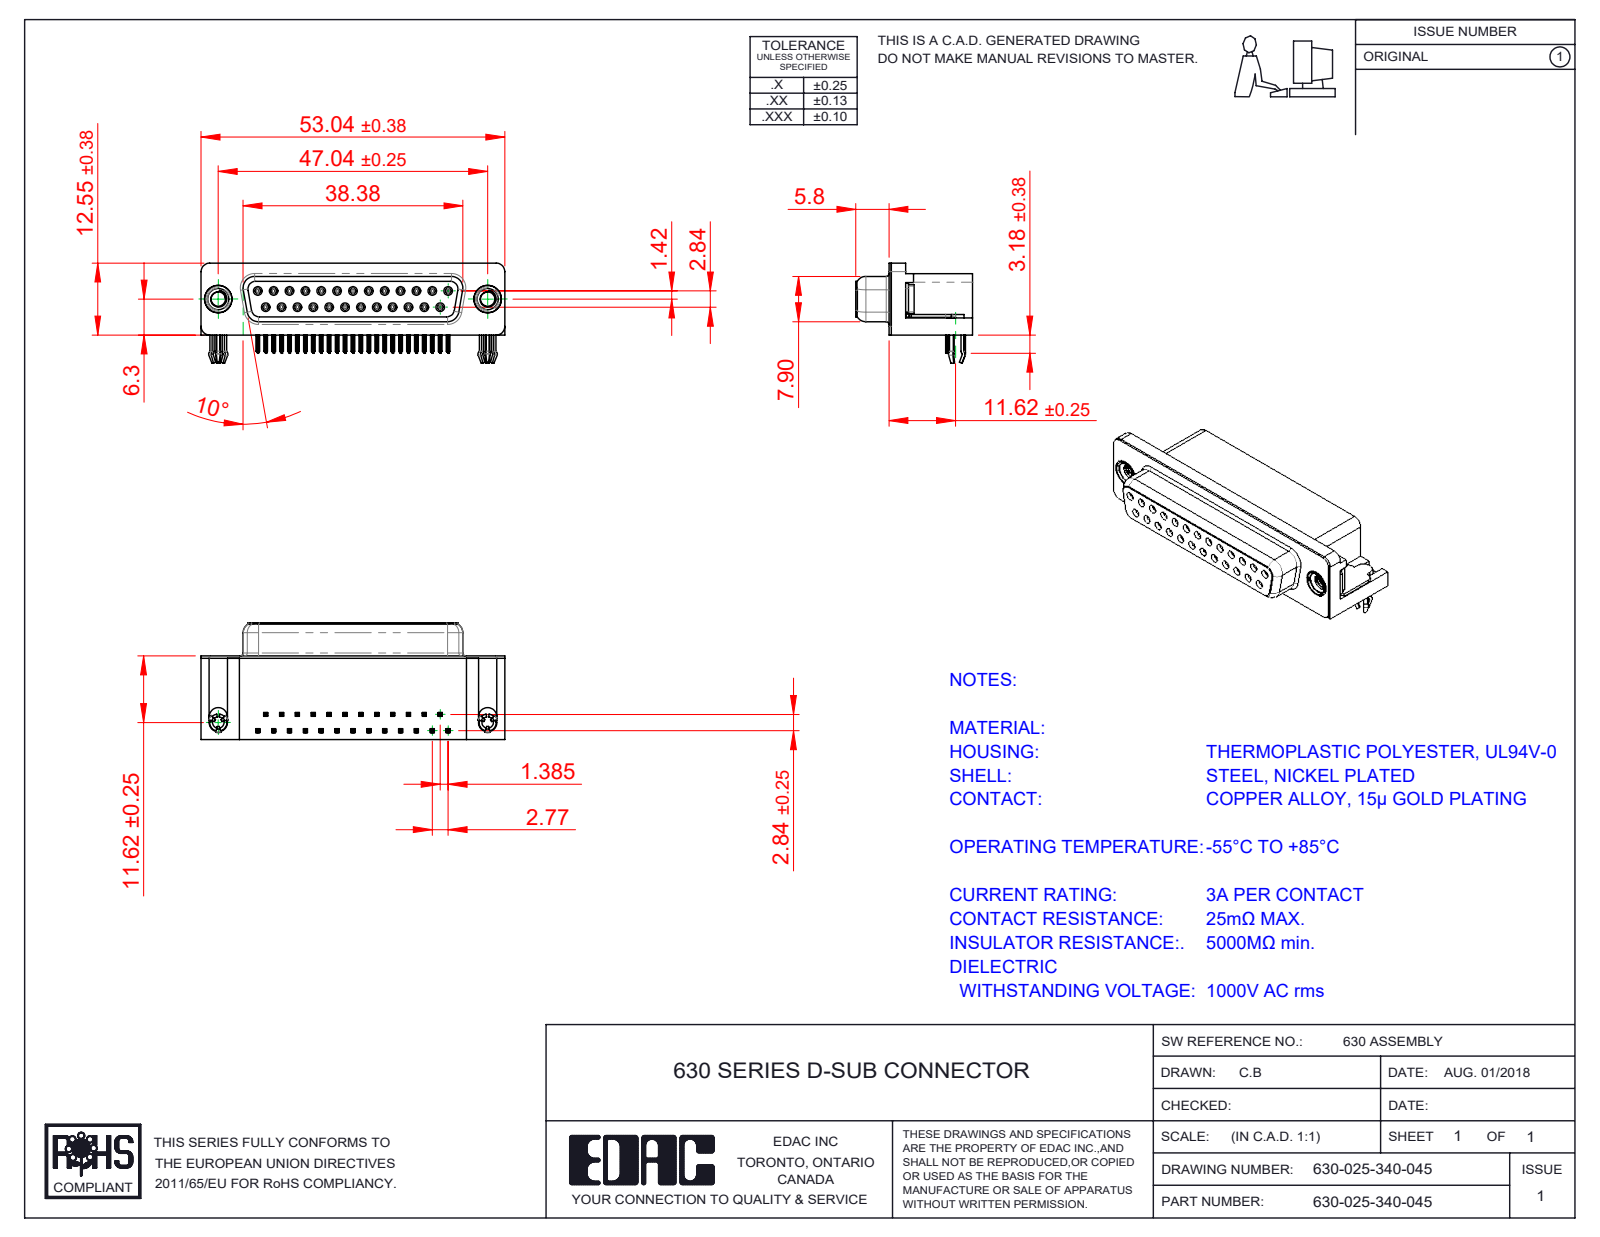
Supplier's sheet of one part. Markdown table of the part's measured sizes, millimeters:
| quantity | value |
| --- | --- |
| part name | 630 Shell_25 Socket; 630 3 Prong Board Lock; 630 M3 Threaded Rivet; 630 Contact Bottom (+3 more) |
| STEP written by | SolidWorks 2020 (CONFIG_CONTROL_DESIGN) |
| units | millimeters |
| bodies | 31 solids, 3954 faces (1760 planar, 930 cylindrical, 1264 other) |
| overall size | 53.04 × 20.4 × 17.48 |
| volume | 8 596 mm³ |
| surface area | 10 169 mm² |
| round holes (diameter × count) | 0.8 × 25, 0.9 × 25, 2 × 2, 2.5 × 2, 4 × 2, 4.8 × 2, 5 × 2 |
| round bosses / shafts (diameter × count) | 1.2 × 25, 4.9 × 2, 4.75 × 2, 3.9 × 2, 3 × 2 |
| partial cylindrical surfaces (radius × count) | 0.1 × 200, 0.15 × 100, 0.35 × 50, 0.34 × 25, 1 × 18, 0.25 × 12, 0.28 × 12, 1.35 × 8 |
| main face-to-face distances | 0.4, 10.35, 6.2, 14.2, 2.73, 0.85, 6.65, 14.6, 2.84, 2.9 |
| hole center spacings | 3.16, 2.77, 5.54, 8.31, 11.08, 5.03, 5.04, 7.48 |
